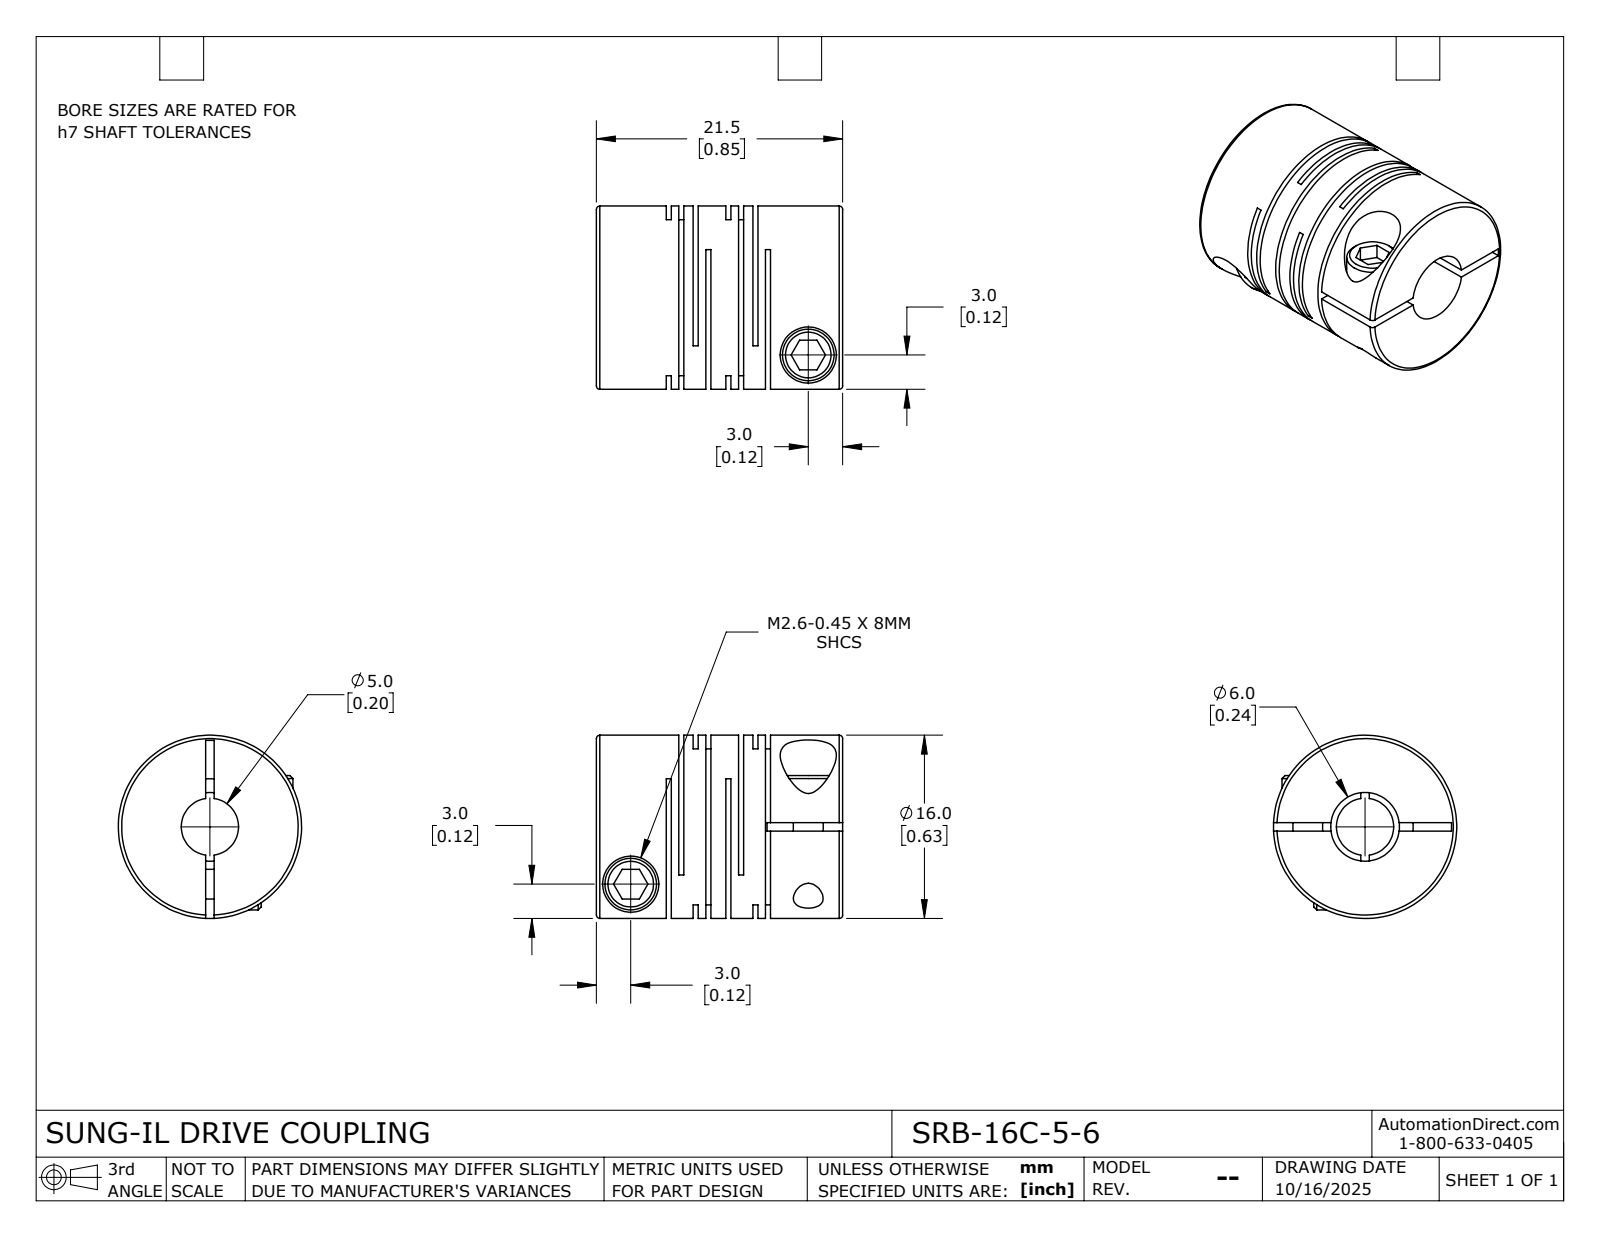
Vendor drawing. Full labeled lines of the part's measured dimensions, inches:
Part name (STEP PRODUCT): SRB-16C-5-6
STEP written by: SolidWorks 2024 (CONFIG_CONTROL_DESIGN)
Units: inches
Bodies: 1 solid, 115 faces (60 planar, 42 cylindrical, 13 other)
Overall size (bounding box): 0.846 × 0.63 × 0.63
Volume: 0.189 in³ · Surface area: 6.591 in²
Round holes (diameter × count): ⌀0.102 ×2, ⌀0.193 ×2, ⌀0.197 ×1, ⌀0.236 ×1
Round bosses / shafts (diameter × count): ⌀0.177 ×2, ⌀0.63 ×1
Main face-to-face distances: 0.043, 0.093, 0.017, 0.205, 0.026, 0.075, 0.188, 0.049, 0.162, 0.113
